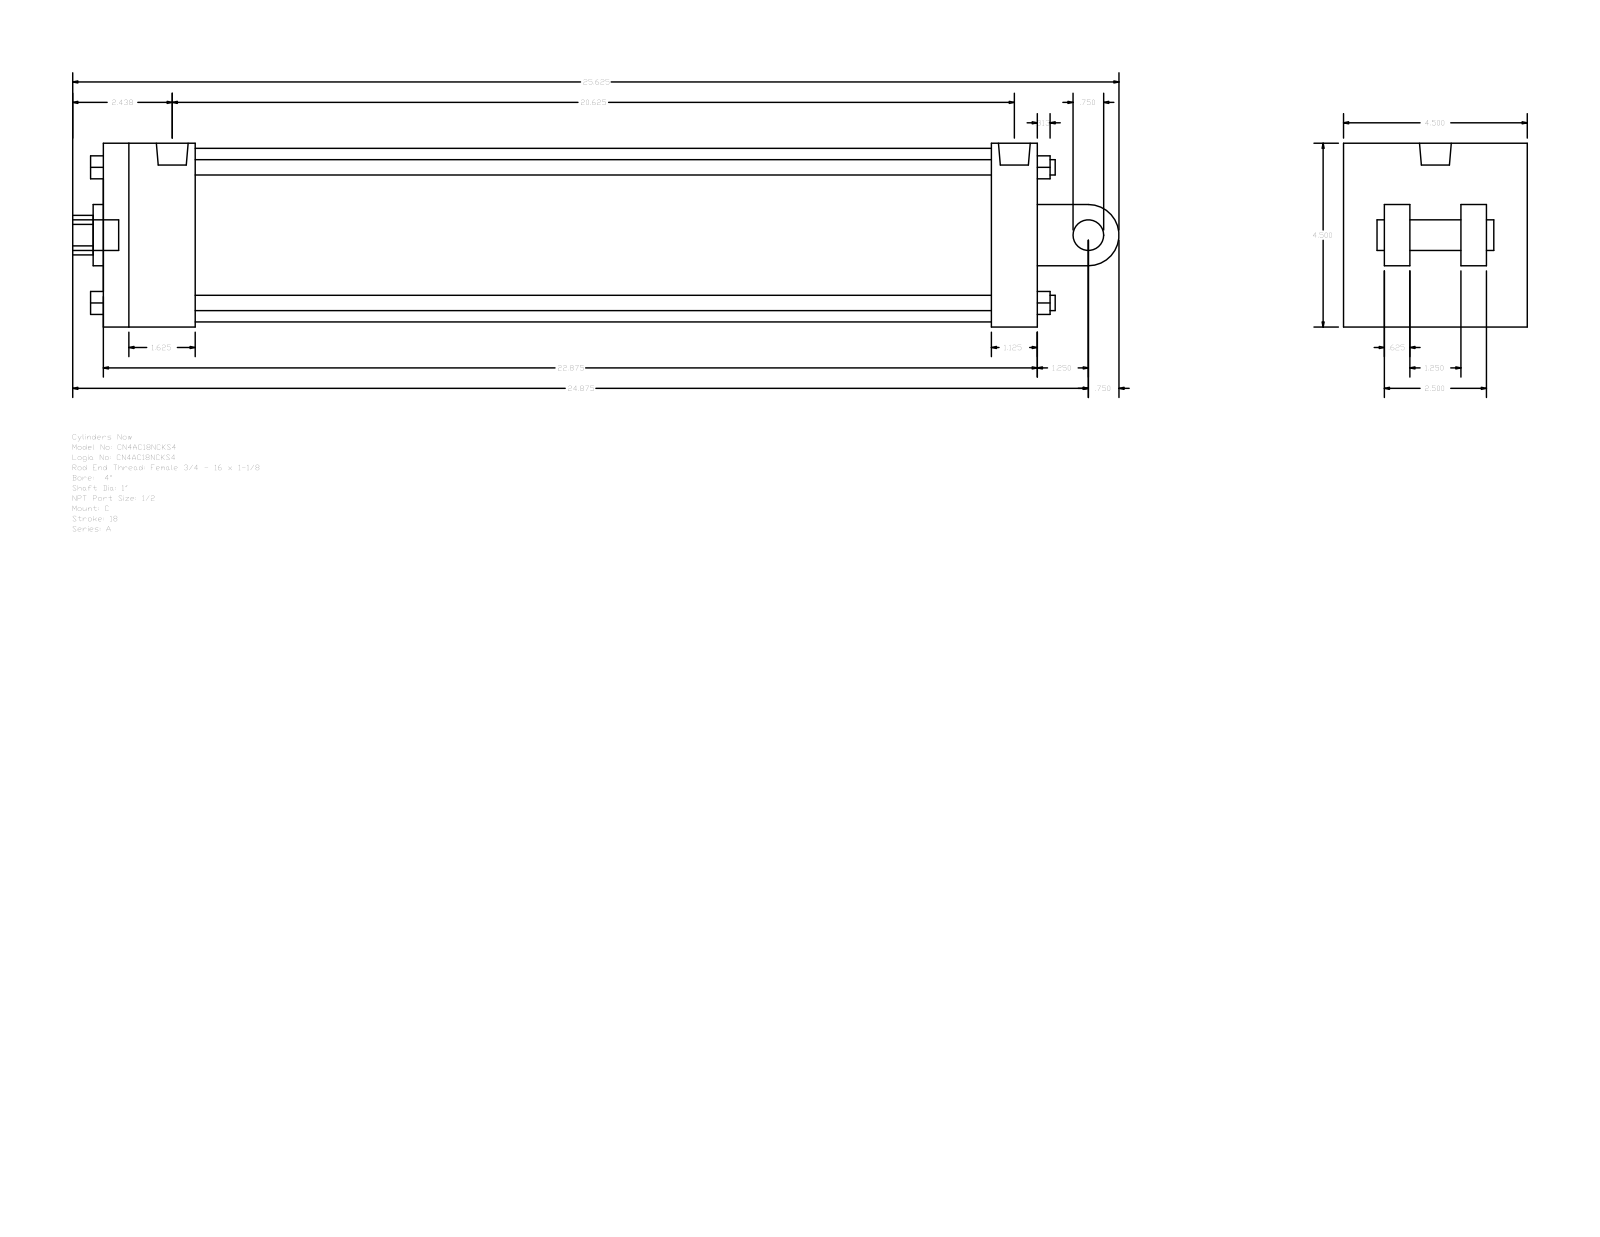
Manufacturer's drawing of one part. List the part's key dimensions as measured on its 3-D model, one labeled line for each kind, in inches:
Part name (STEP PRODUCT): A_C__0400_1
STEP written by: GSSL Pune (CONFIG_CONTROL_DESIGN)
Units: inches
Bodies: 0 solids, 135 faces (102 planar, 33 cylindrical, 0 other)
Overall size (bounding box): 25.625 × 4.5 × 4.5
Round holes (diameter × count): ⌀0.344 ×2, ⌀0.778 ×1, ⌀1 ×1, ⌀1.5 ×1, ⌀4.25 ×1
Round bosses / shafts (diameter × count): ⌀0.375 ×4, ⌀0.75 ×2, ⌀0.344 ×2, ⌀0.778 ×1
Partial cylindrical surfaces — rounded edges, fillets, slot ends (radius × count): R0.484 ×1, R0.75 ×1
Main face-to-face distances: 4.5, 22.875, 2.875, 21.75, 1.125, 2.25, 19.5, 20.625, 0.625, 1.875
Hole centre spacings: 0.125
